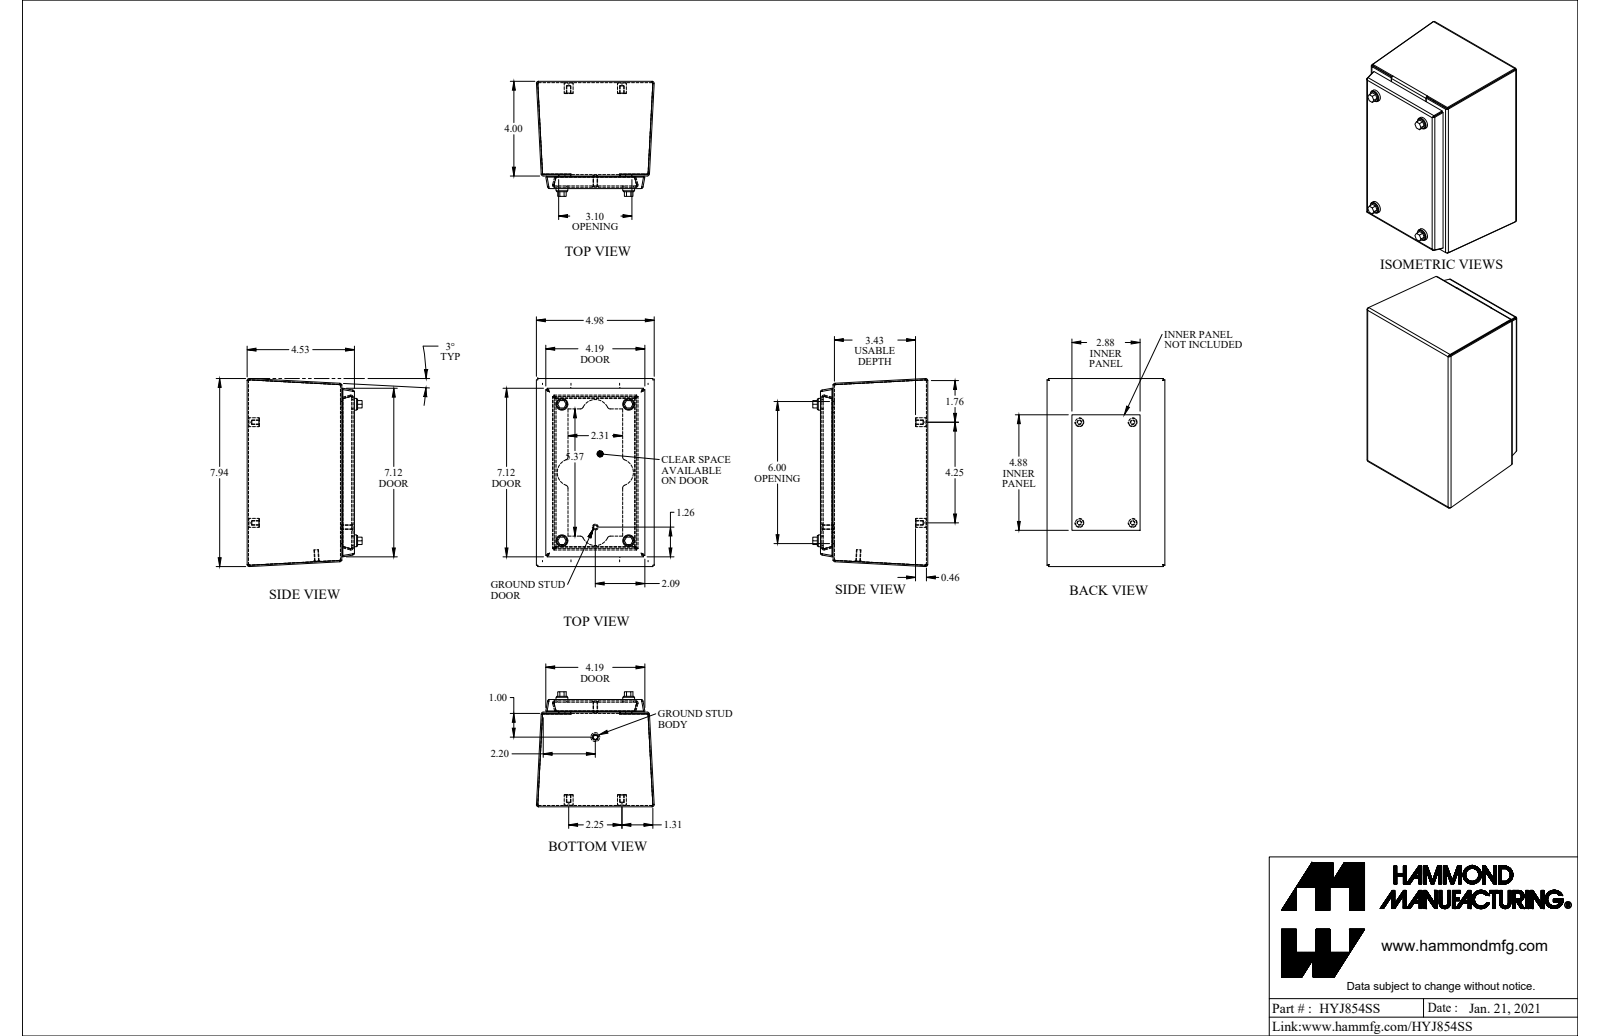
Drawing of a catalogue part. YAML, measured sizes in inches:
part_name: "HYJ854SS"
step_written_by: "SolidWorks 2021 (AUTOMOTIVE_DESIGN)"
units: inches
bodies: {solids: 26, faces: 477, planar: 305, cylindrical: 140, other: 32}
overall_size: [7.942, 4.976, 4.859]
volume: 14.94
surface_area: 477.6
round_holes:
  - {diameter: 0.065, count: 4}
  - {diameter: 0.156, count: 4}
  - {diameter: 0.235, count: 4}
  - {diameter: 0.239, count: 4}
  - {diameter: 0.24, count: 4}
  - {diameter: 0.25, count: 4}
  - {diameter: 0.253, count: 4}
  - {diameter: 0.4, count: 4}
round_bosses_or_shafts:
  - {diameter: 0.375, count: 8}
  - {diameter: 0.19, count: 6}
  - {diameter: 0.5, count: 4}
  - {diameter: 0.45, count: 4}
  - {diameter: 0.406, count: 4}
  - {diameter: 0.315, count: 4}
  - {diameter: 0.25, count: 2}
partial_cylinders:
  - {radius: 0.029, count: 16}
  - {radius: 0.086, count: 16}
  - {radius: 0.125, count: 12}
  - {radius: 0.055, count: 4}
  - {radius: 0.076, count: 4}
  - {radius: 0.5, count: 4}
  - {radius: 0.575, count: 4}
face_to_face_distances: [0.057, 4.418, 4.475, 0.057, 3.943, 4.532, 4.475, 0.475, 4, 0.532]
hole_center_spacings: [6.418, 5.766, 2.819, 5.613, 5.766, 2.819, 2.645, 5.016]
